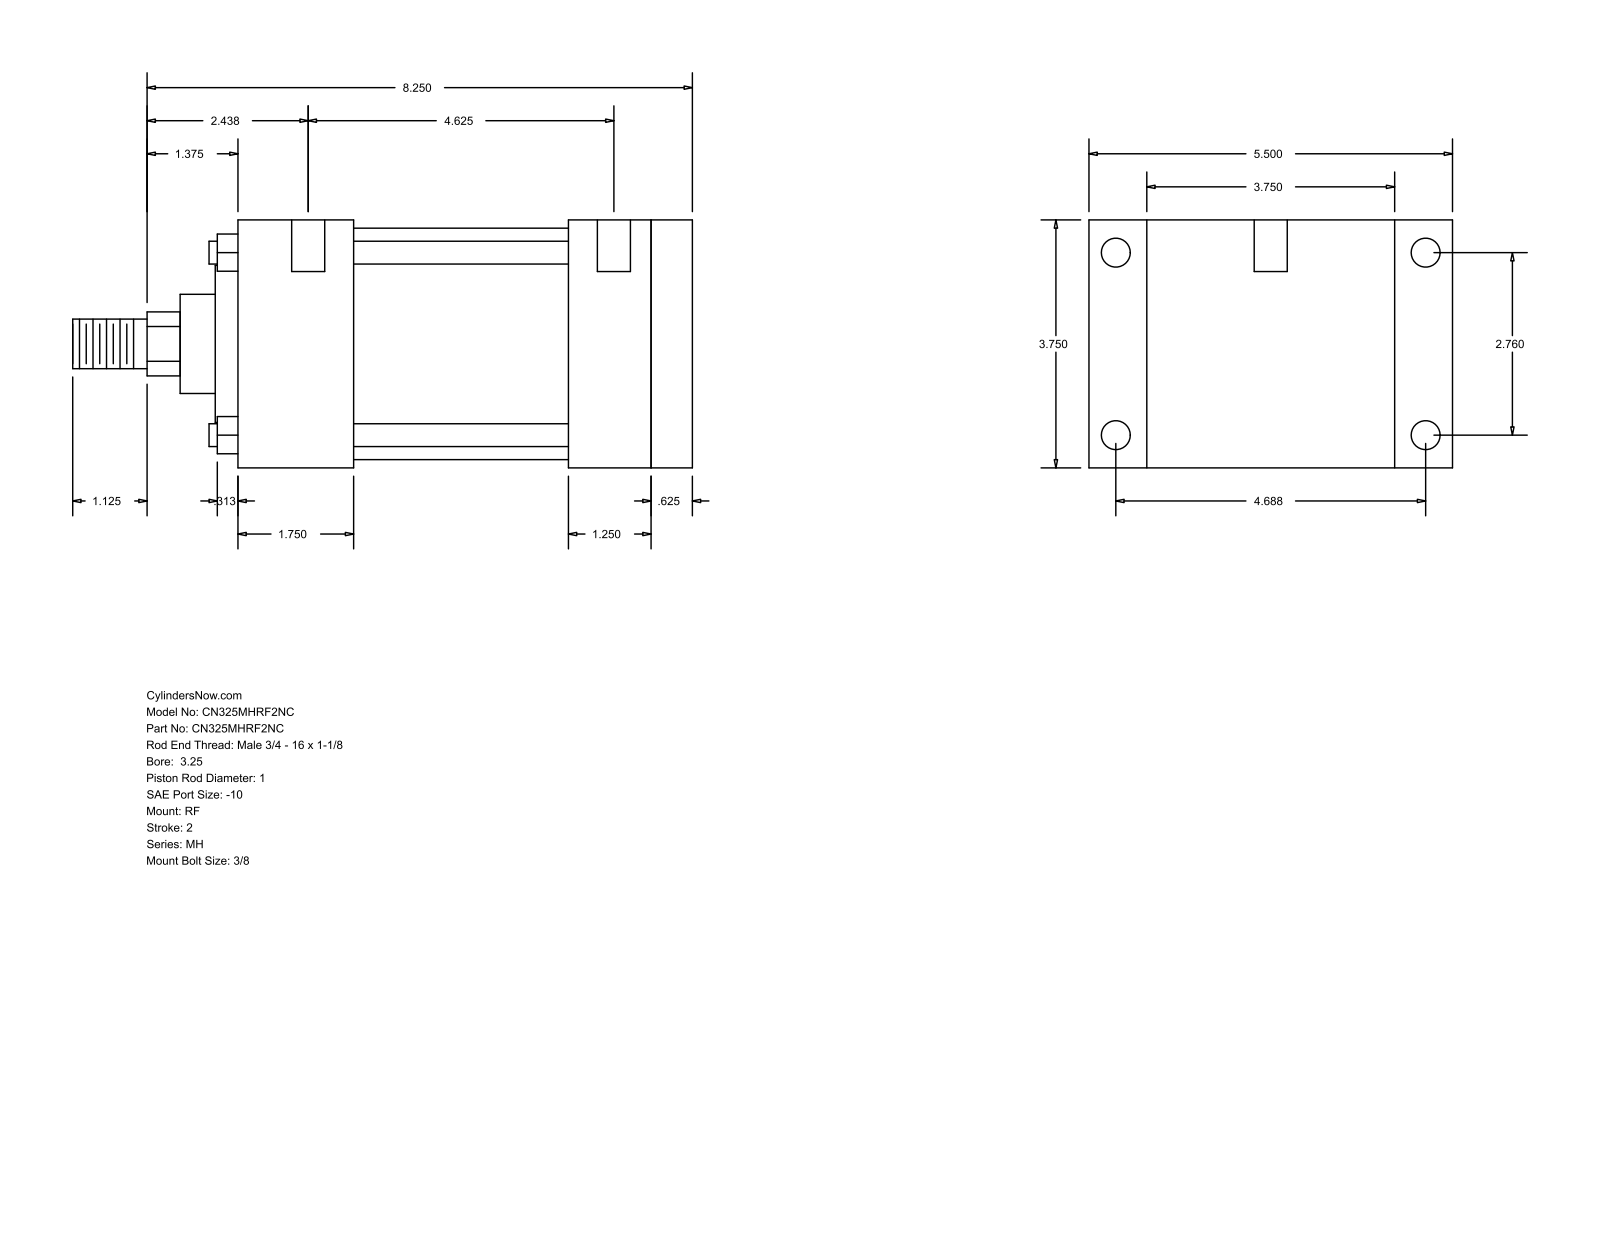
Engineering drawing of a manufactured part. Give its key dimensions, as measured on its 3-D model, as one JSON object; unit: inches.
{"part_name": "MH_RF__0325_1", "step_written_by": "GSSL Pune (CONFIG_CONTROL_DESIGN)", "units": "inches", "bodies": {"solids": 0, "faces": 94, "planar": 65, "cylindrical": 29, "other": 0}, "overall_size": [9.375, 5.5, 3.75], "round_holes": [[0.219, 4], [0.438, 4], [0.5, 2]], "round_bosses_or_shafts": [[0.345, 4], [3.5, 1], [2.375, 1], [1.5, 1], [1, 1], [0.75, 1]], "partial_cylinders_radius": [[0.484, 1]], "face_to_face_distances": [3.75, 6.875, 6.25, 0.625, 0.875, 4.625, 1.75, 4.5, 5.125, 5], "hole_center_spacings": [4.687, 2.76, 4.875, 5.439, 0.062, 0.187, 4.625, 4.813]}
